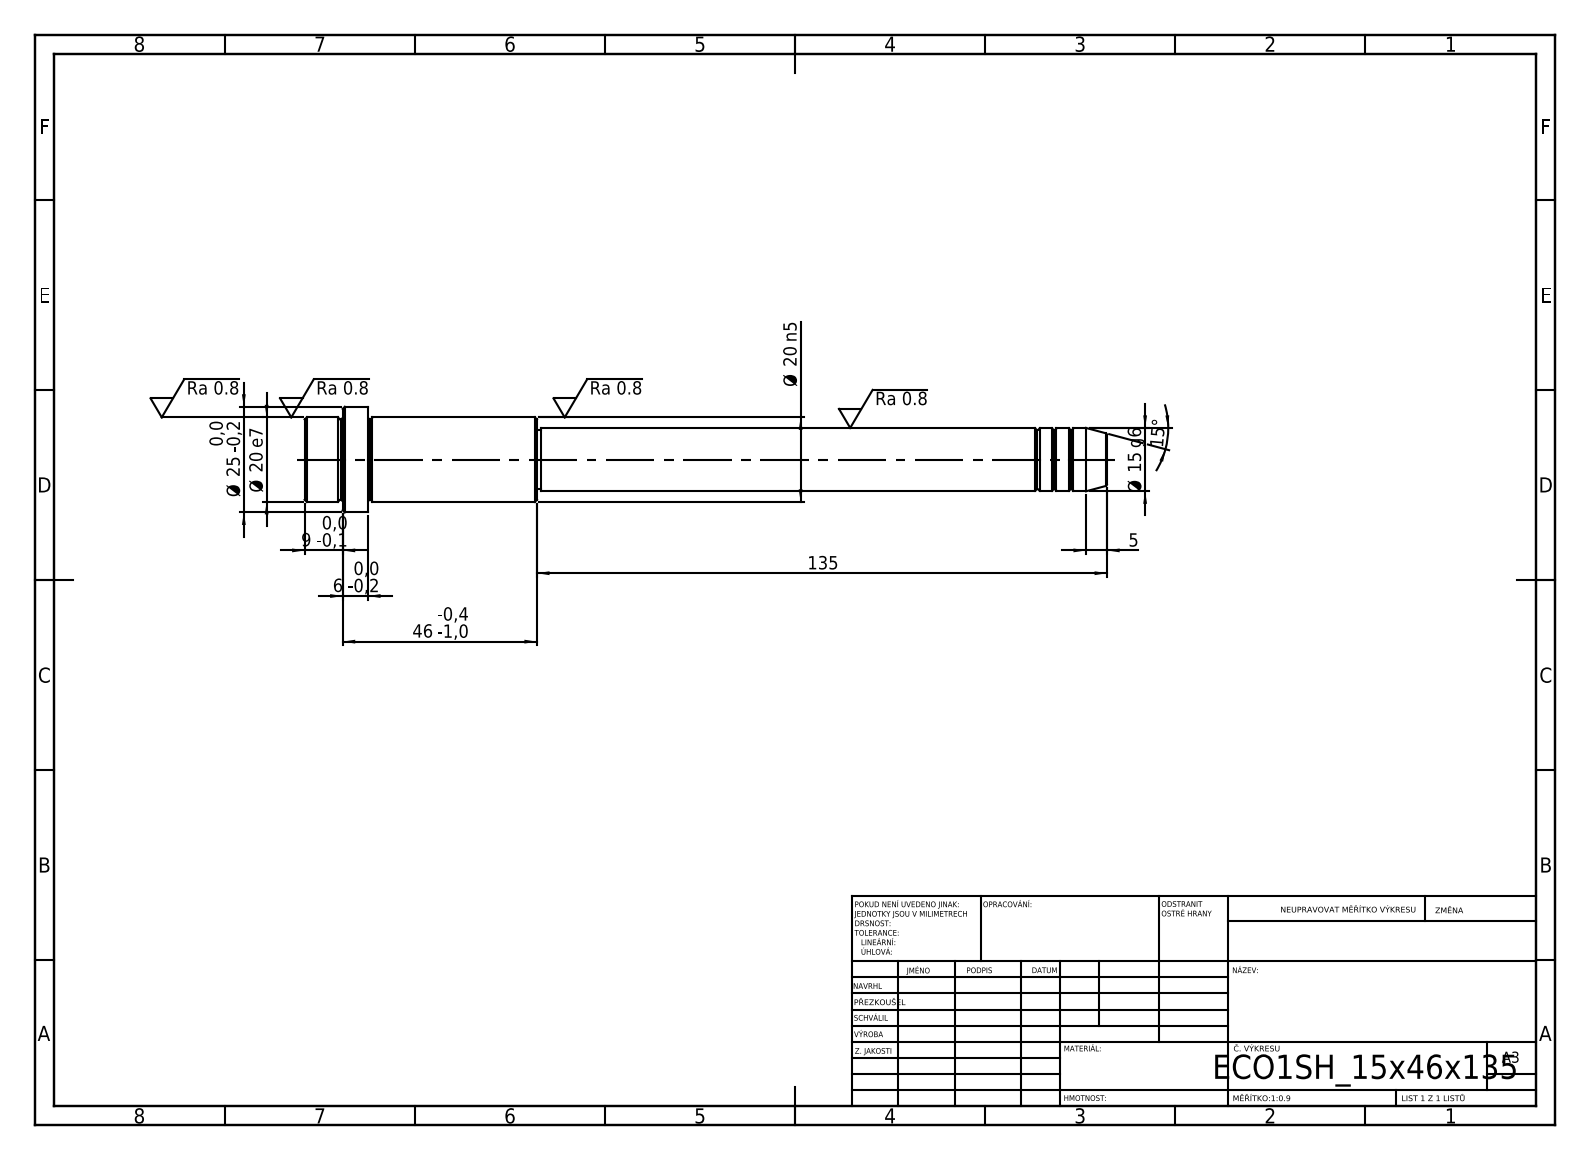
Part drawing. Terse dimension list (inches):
written by: SolidWorks 2019 (CONFIG_CONTROL_DESIGN)
unit: in
bodies: 1 solid, 52 faces (6 planar, 16 cylindrical, 30 other)
size: 7.48 × 0.984 × 0.984
volume: 2.557 in³; area: 16.95 in²
bosses: 1× ⌀0.984, 1× ⌀0.787, 1× ⌀0.591, 1× ⌀0.551
face distances: 0.591, 0.236, 0.354, 1.575, 1.811, 2.165, 5.315, 6.89, 7.126, 7.48
